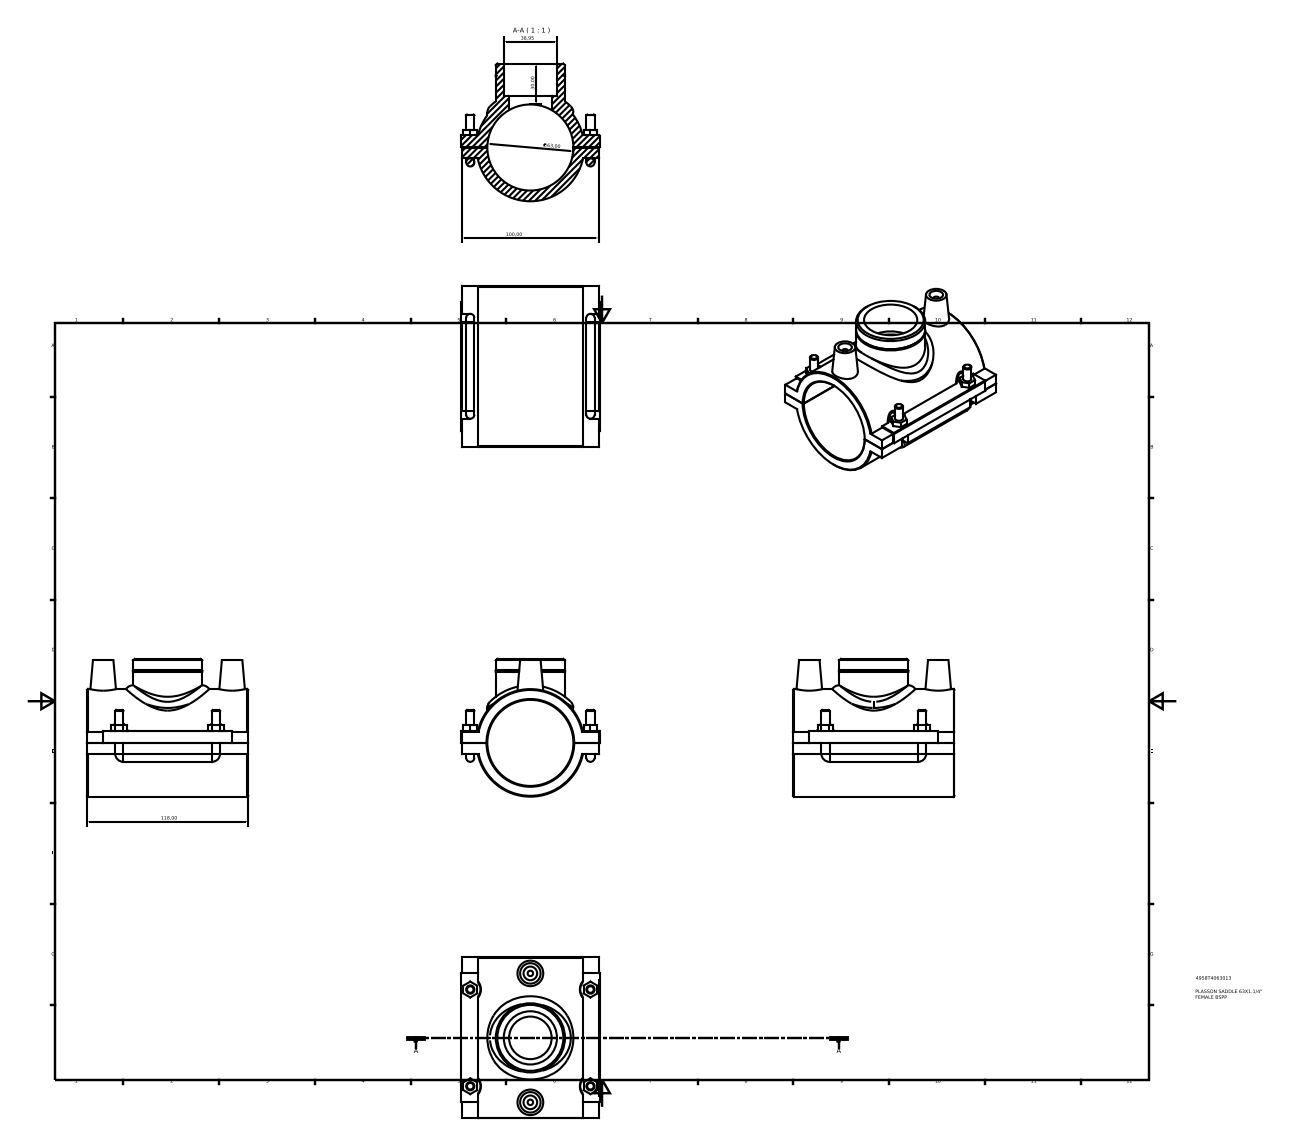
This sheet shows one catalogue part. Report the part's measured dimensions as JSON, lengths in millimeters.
{"part_name": "4958T4063013", "step_written_by": "Autodesk Inventor 2015 (AUTOMOTIVE_DESIGN)", "units": "millimeters", "bodies": {"solids": 1, "faces": 142, "planar": 82, "cylindrical": 34, "other": 26}, "overall_size": [118, 102, 100.88], "volume_mm3": 282208, "surface_area_mm2": 84561, "round_holes": [[10, 2], [31.16, 1], [38.95, 1], [63, 1]], "round_bosses_or_shafts": [[6, 6], [4, 2], [78.75, 1], [50.64, 1], [49.64, 1]], "partial_cylinders_radius": [[7.5, 4], [0.5, 1], [31.5, 1], [42.21, 1]], "face_to_face_distances": [7.83, 7.93, 1, 16.75, 8.92, 8.82, 118, 101, 100, 52.63], "hole_center_spacings": [47.2, 94.4]}
